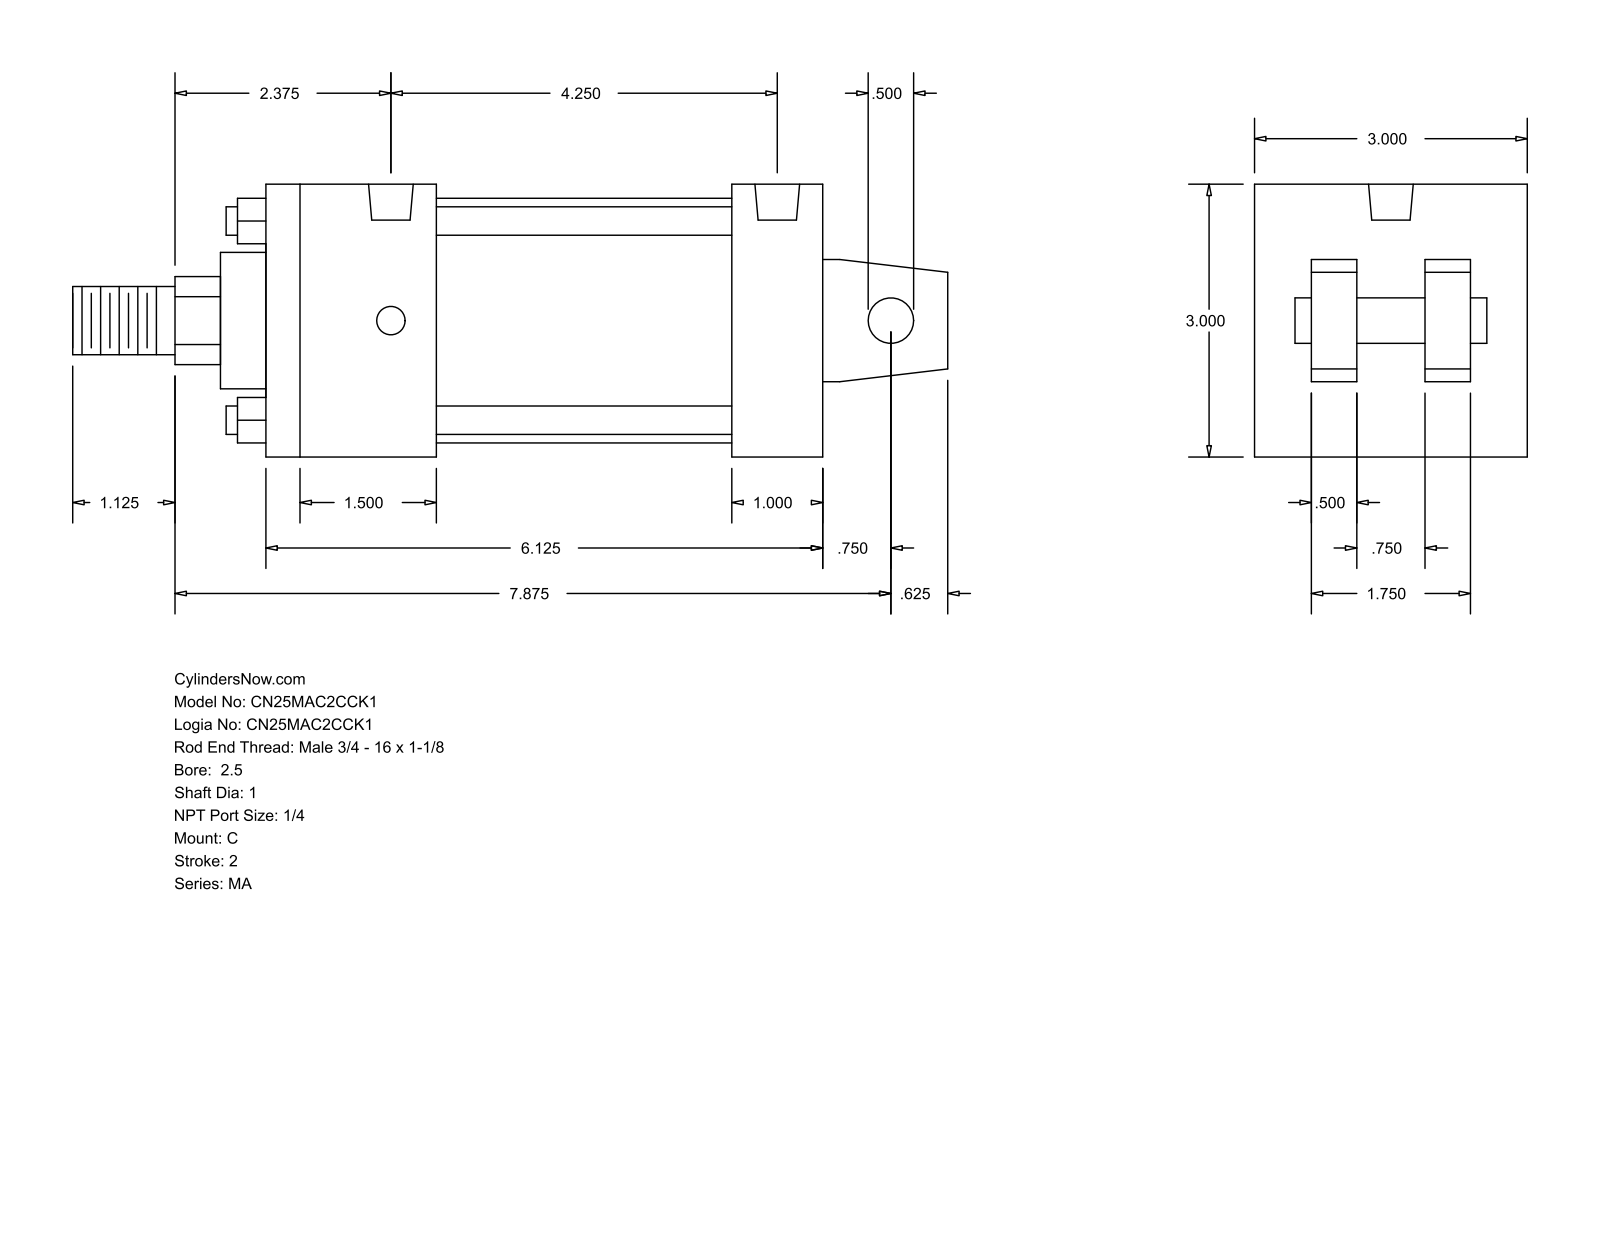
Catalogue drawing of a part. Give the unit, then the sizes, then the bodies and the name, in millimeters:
Units: millimetres
Overall size (bounding box): 244.47 × 76.2 × 76.2
Round holes (diameter × count): ⌀7.94 ×4, ⌀12.49 ×2
Round bosses / shafts (diameter × count): ⌀7.94 ×4, ⌀68.33 ×1, ⌀38.1 ×1, ⌀25.4 ×1, ⌀19.05 ×1, ⌀12.7 ×1
Partial cylindrical surfaces — rounded edges, fillets, slot ends (radius × count): R12.29 ×1
Main face-to-face distances: 76.2, 155.57, 47.63, 12.7, 60.33, 15.87, 25.4, 28.57, 130.17, 82.54
Hole centre spacings: 107.95
Bodies: 0 solids, 103 faces (76 planar, 27 cylindrical, 0 other)
Part name (STEP PRODUCT): MA_C__0250_1
STEP written by: GSSL Pune (CONFIG_CONTROL_DESIGN)
